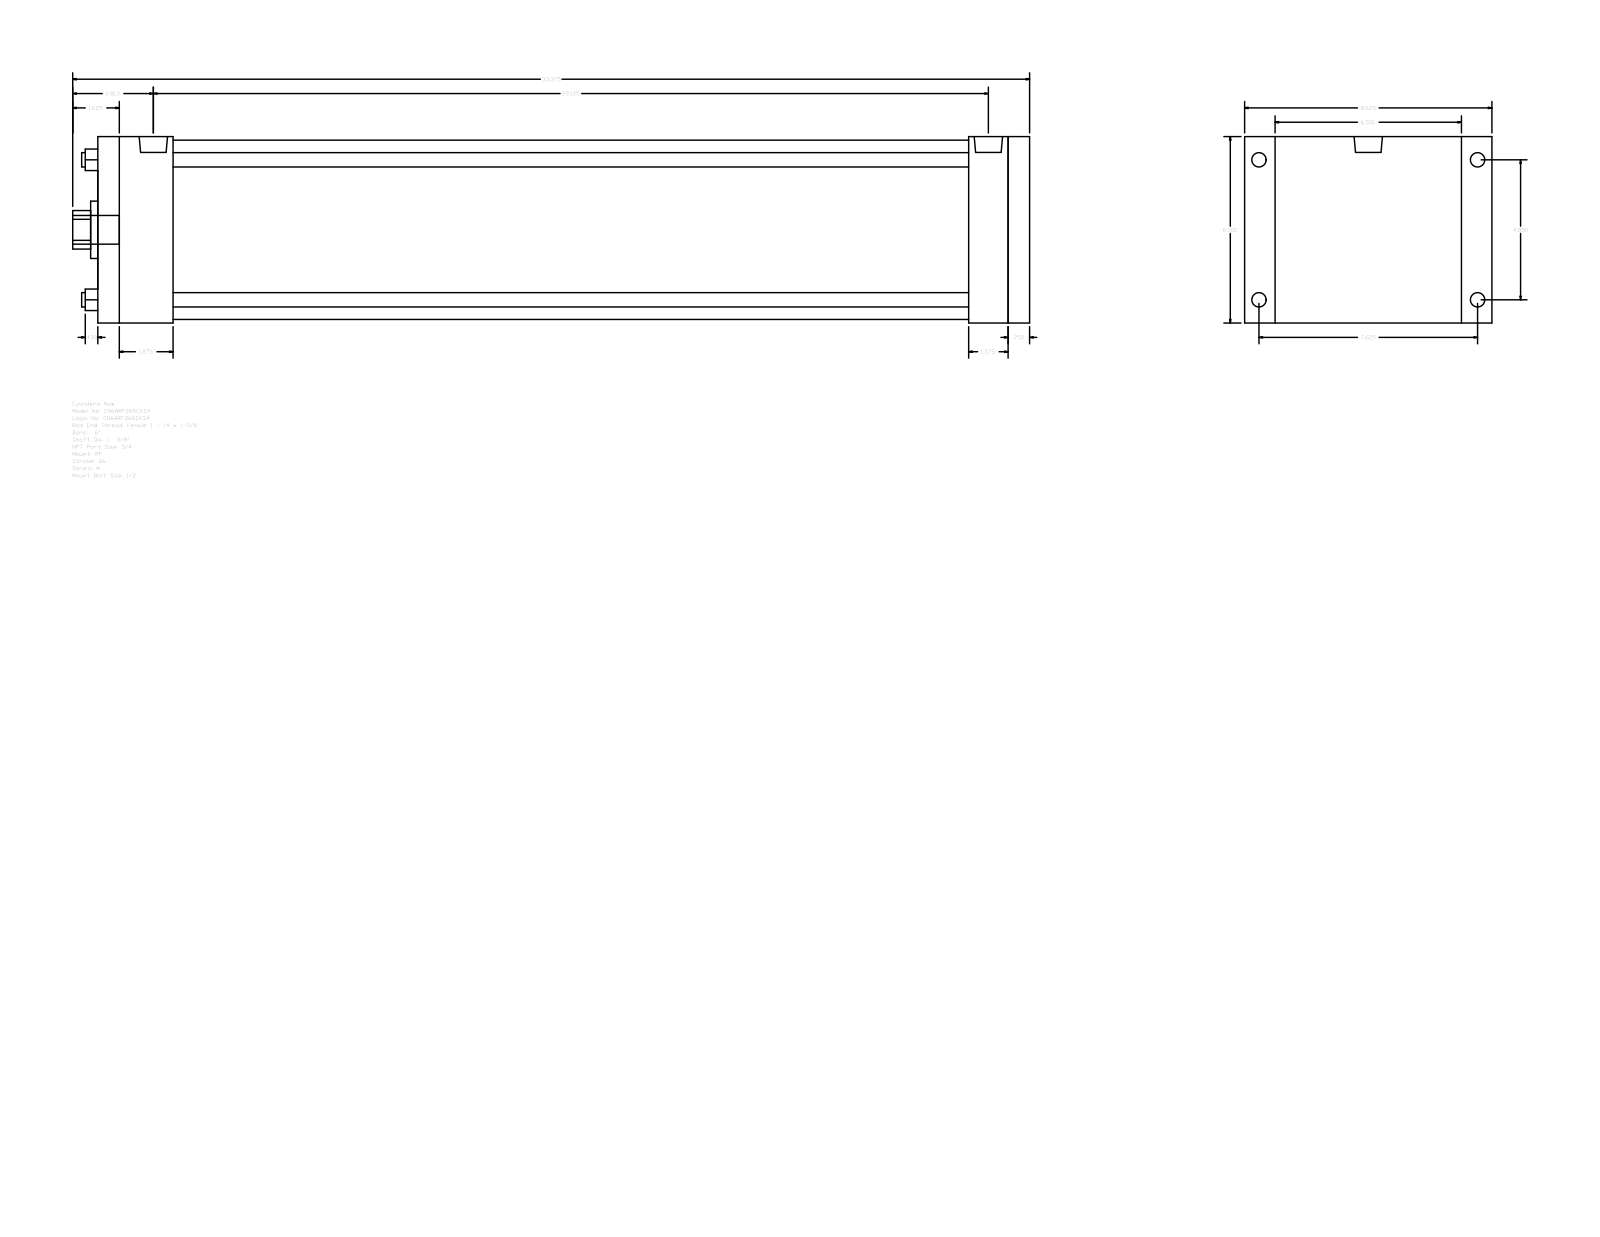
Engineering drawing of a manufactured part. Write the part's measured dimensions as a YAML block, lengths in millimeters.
part_name: "A_RF__0600_1.375"
step_written_by: "GSSL Pune (CONFIG_CONTROL_DESIGN)"
units: millimeters
bodies: {solids: 0, faces: 92, planar: 64, cylindrical: 28, other: 0}
overall_size: [847.73, 219.07, 165.1]
round_holes:
  - {diameter: 12.7, count: 4}
  - {diameter: 34.92, count: 1}
  - {diameter: 50.8, count: 1}
  - {diameter: 158.75, count: 1}
round_bosses_or_shafts:
  - {diameter: 15.08, count: 4}
  - {diameter: 12.7, count: 4}
  - {diameter: 25.12, count: 2}
  - {diameter: 25.4, count: 1}
partial_cylinders:
  - {radius: 17.06, count: 1}
face_to_face_distances: [165.1, 825.5, 806.44, 19.06, 66.67, 739.77, 758.83, 771.52, 704.85, 34.92]
hole_center_spacings: [87.65, 123.96, 175.31]
